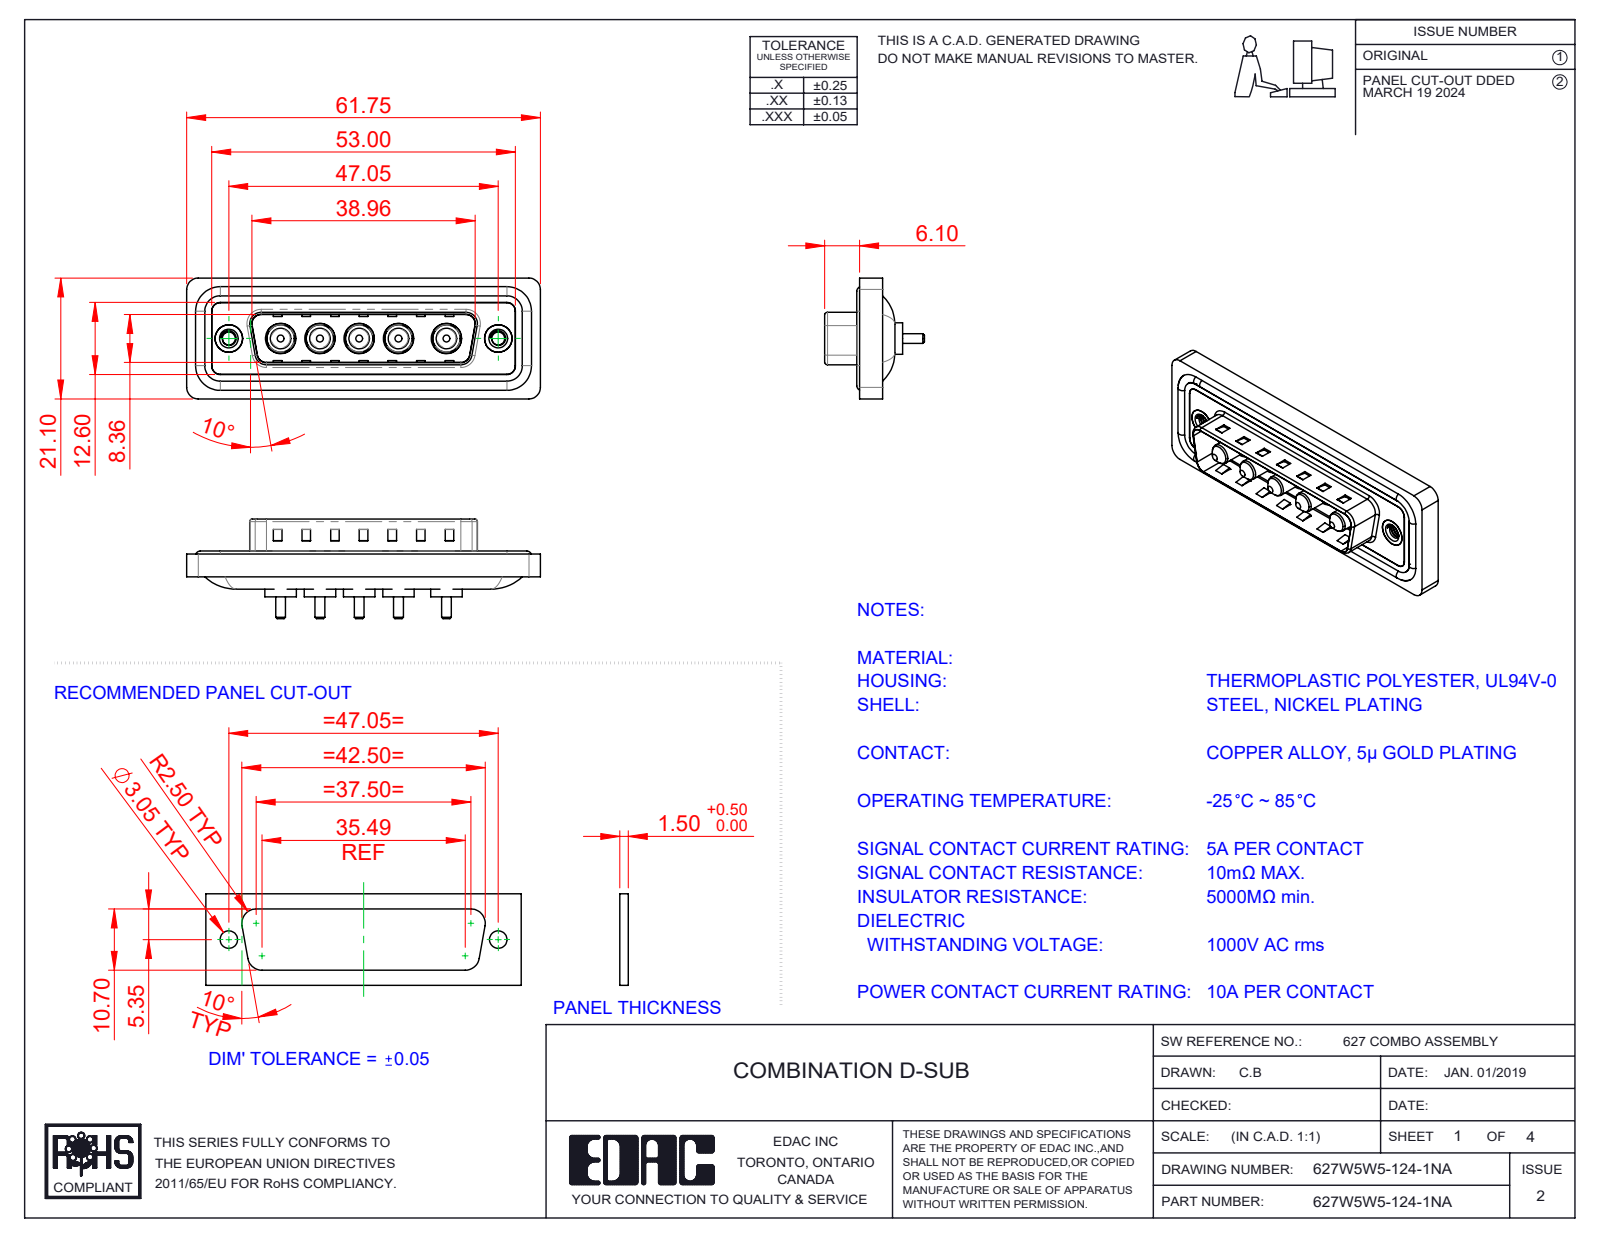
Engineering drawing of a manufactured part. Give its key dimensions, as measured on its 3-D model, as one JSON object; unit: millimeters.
{"part_name": "627W5W5-124-1NA; 627Combo Threaded Rivet_A; 627Combo Shell Rear_25 Contacts; Power Pin_10A S (+3 more)", "step_written_by": "SolidWorks 2023 (CONFIG_CONTROL_DESIGN)", "units": "millimeters", "bodies": {"solids": 17, "faces": 676, "planar": 259, "cylindrical": 285, "other": 132}, "overall_size": [61.75, 21.1, 17.4], "volume_mm3": 7401, "surface_area_mm2": 11731, "round_holes": [[4.85, 5], [5.3, 5], [2.26, 2], [4, 2], [4.8, 2], [5, 2]], "round_bosses_or_shafts": [[5.5, 5], [5.2, 5], [4.75, 5], [3.75, 5], [3.6, 5], [1.7, 5], [1.6, 4], [4.9, 2]], "partial_cylinders_radius": [[1.5, 22], [2, 18], [0.5, 8], [1.6, 8], [2.1, 5], [0.25, 4], [0.6, 4], [0.65, 4]], "face_to_face_distances": [0.4, 1.5, 0.5, 1.1, 3.1, 1.6, 2.9, 0.82, 9.58, 5.65], "hole_center_spacings": [6.86, 9.04, 13.73, 38.01, 6.87, 8.37, 8.38, 9.05]}
